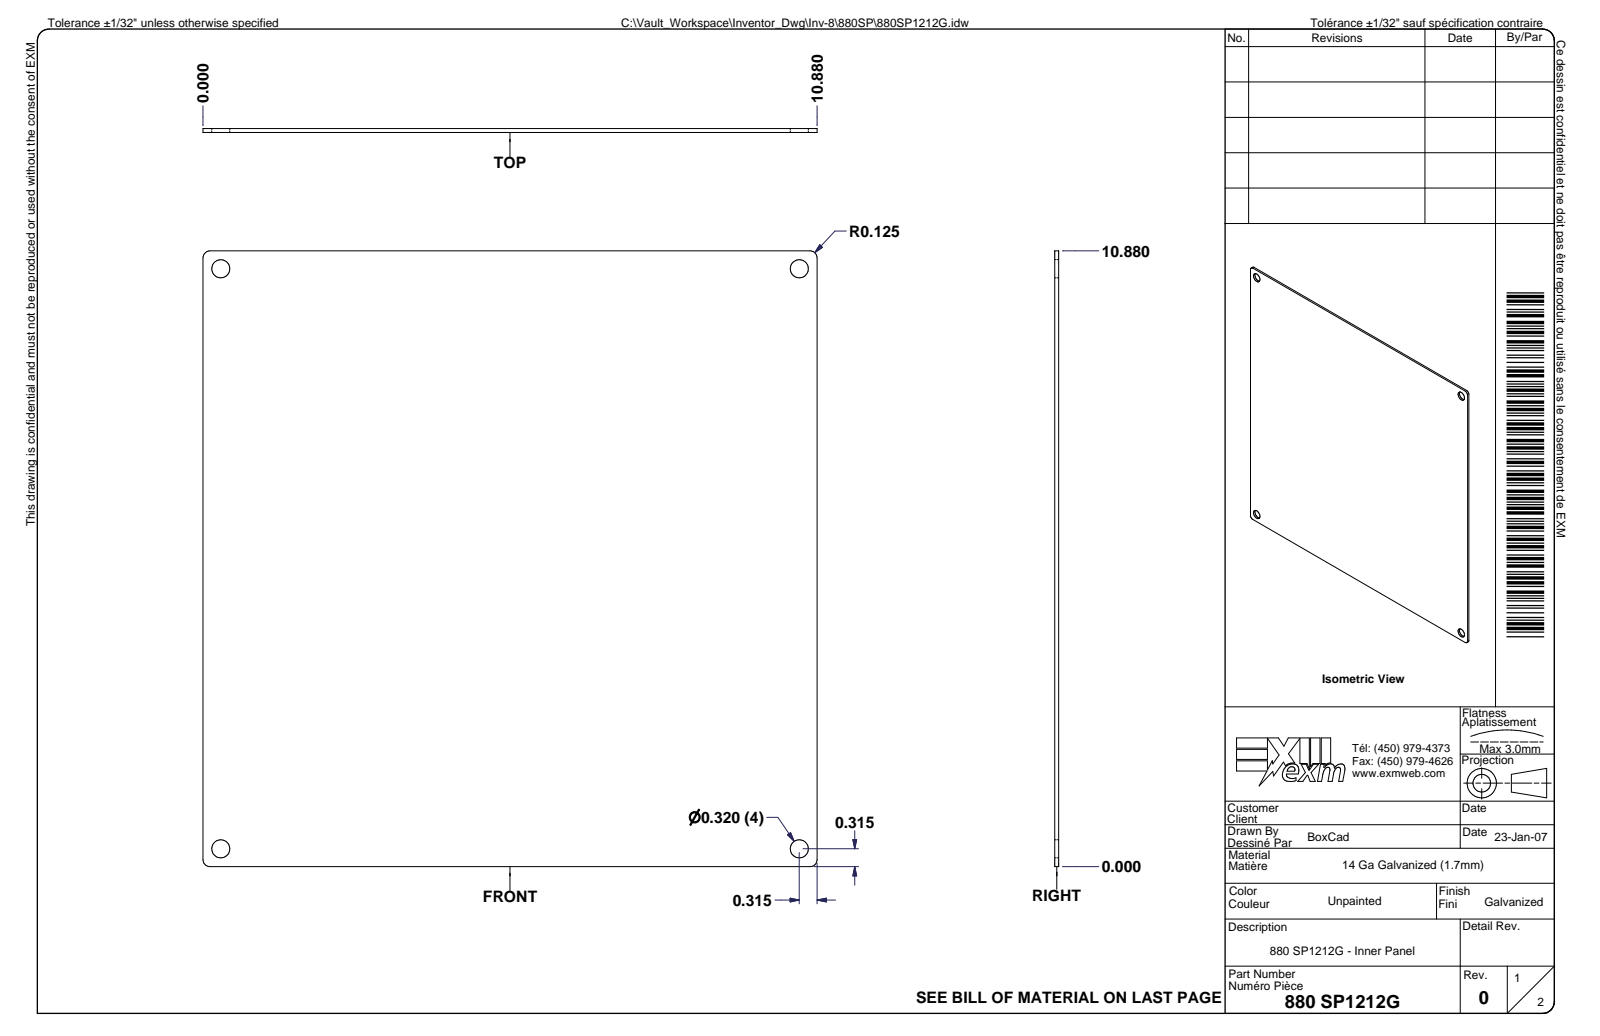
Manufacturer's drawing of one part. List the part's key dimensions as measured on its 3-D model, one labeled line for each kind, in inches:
Part name (STEP PRODUCT): 5412CH121204; 5412CH121204B; 5412CH121204B-P; STK-Q-08350 (+8 more)
STEP written by: Autodesk Inventor 2024 (AUTOMOTIVE_DESIGN)
Units: inches
Bodies: 59 solids, 7325 faces (3663 planar, 1502 cylindrical, 2160 other)
Overall size (bounding box): 13.496 × 12.757 × 4.451
Volume: 43.26 in³ · Surface area: 1 462 in²
Round holes (diameter × count): ⌀0.201 ×12, ⌀0.03 ×6, ⌀0.24 ×6, ⌀0.311 ×5, ⌀0.305 ×4, ⌀0.32 ×4, ⌀0.394 ×3, ⌀0.165 ×2, ⌀0.173 ×2, ⌀0.175 ×2, ⌀0.236 ×2, ⌀0.127 ×1
Round bosses / shafts (diameter × count): ⌀0.232 ×9, ⌀0.035 ×6, ⌀0.512 ×5, ⌀0.39 ×4, ⌀0.197 ×3, ⌀0.394 ×2, ⌀0.3 ×2, ⌀0.193 ×2
Partial cylindrical surfaces — rounded edges, fillets, slot ends (radius × count): R0.02 ×225, R0.008 ×80, R0.039 ×70, R0.01 ×67, R0.012 ×67, R0.004 ×45, R0.079 ×29, R0.197 ×21
Main face-to-face distances: 0.055, 4.126, 11.945, 4.181, 4.071, 0.469, 0.413, 3.658, 3.713, 0.536
Hole centre spacings: 10.25, 10.139, 10.25, 0.546, 10.781, 14.495, 14.79, 0.545
